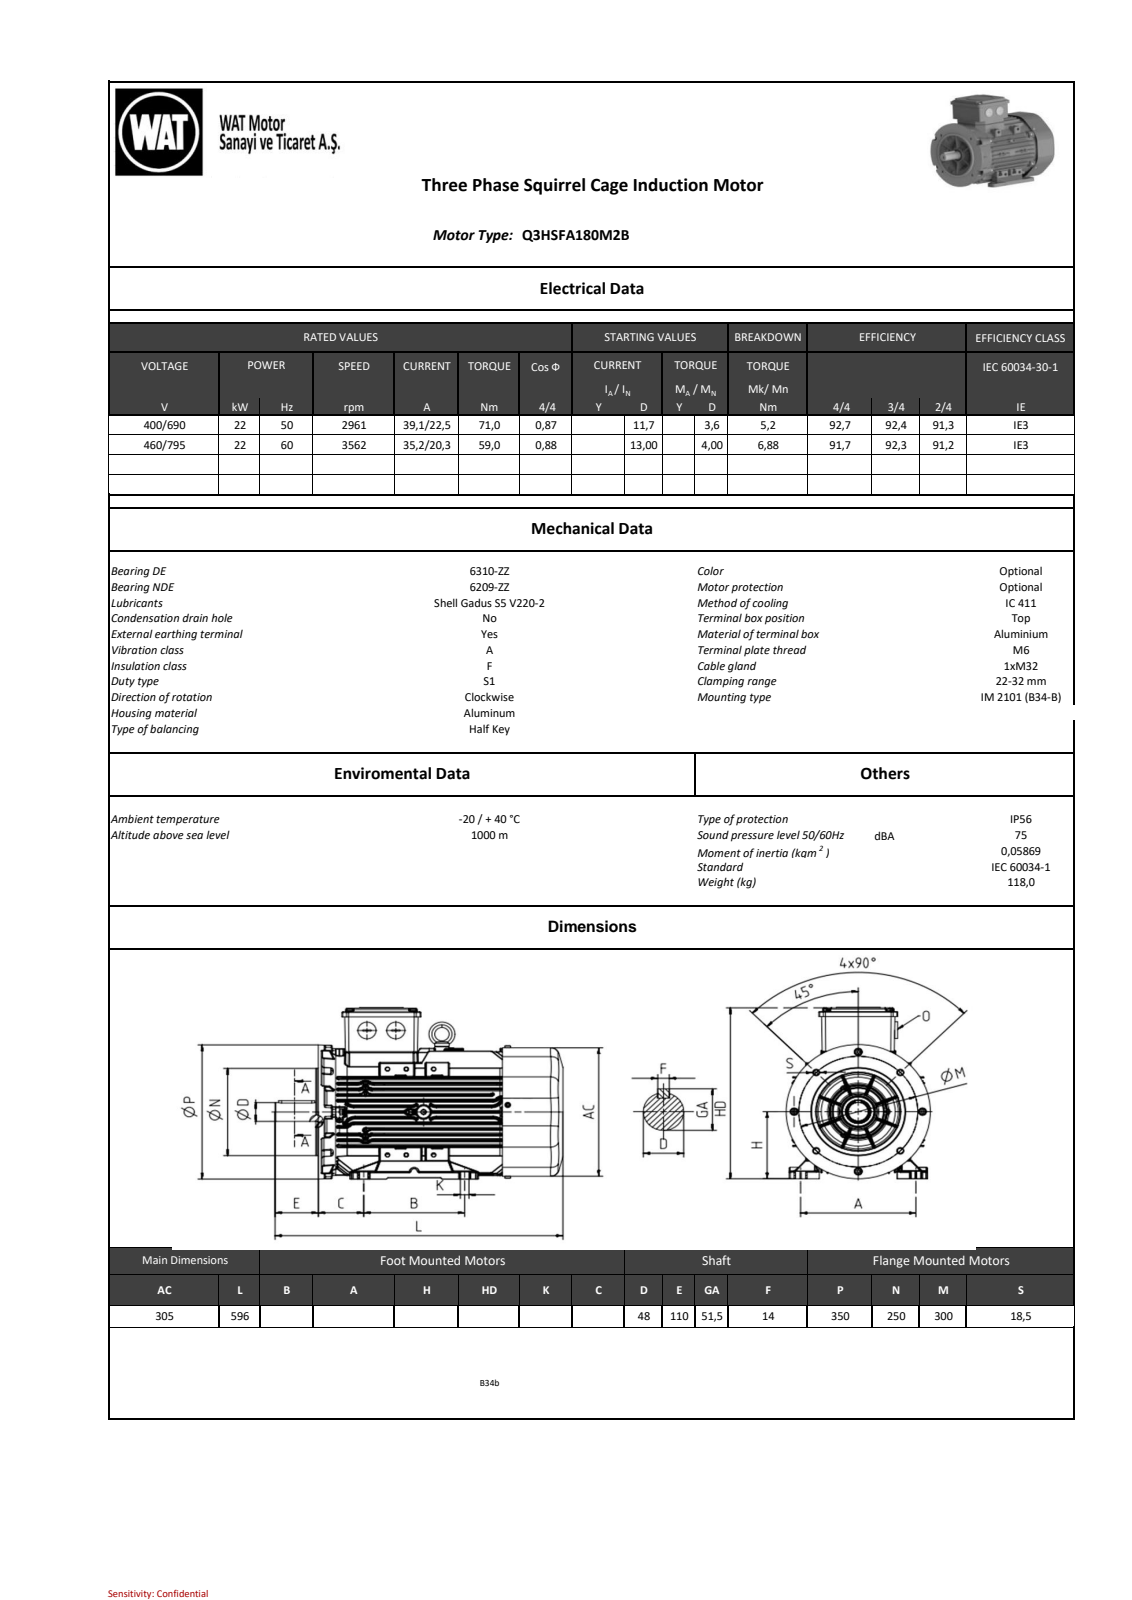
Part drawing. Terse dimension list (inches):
name: 001_objects
written by: SIEMENS PLM Software NX2206.8101 (AP203_CONFIGURATION_CONTROLLED_3D_DESIGN_OF_MECHANICAL_PARTS_AND_ASSEMBLIES_MIM_LF)
unit: in
bodies: 0 solids, 6471 faces (1564 planar, 2739 cylindrical, 2168 other)
size: 23.463 × 15.461 × 13.775
holes: 5× ⌀0.669, 1× ⌀0.394, 1× ⌀1.346, 1× ⌀3.15, 1× ⌀3.371, 1× ⌀3.701, 1× ⌀4.488, 1× ⌀5.276, 1× ⌀6.063, 1× ⌀6.85, 1× ⌀7.638
bosses: 4× ⌀0.315, 2× ⌀1.496, 1× ⌀10.728, 1× ⌀9.843, 1× ⌀7.008, 1× ⌀6.614, 1× ⌀6.22, 1× ⌀5.433
rounds: 732× R0.02, 372× R0.039, 112× R0.079, 91× R0.118, 75× R0.157, 64× R0.098, 43× R0.197, 20× R0.217
face distances: 0.467, 6.515, 5.669, 6.614, 0.367, 0.1, 6.148, 0.469, 0.059, 0.845
hole spacings: 5.61, 7.934, 5.603, 5.604, 5.617, 5.618, 11.22, 5.602
